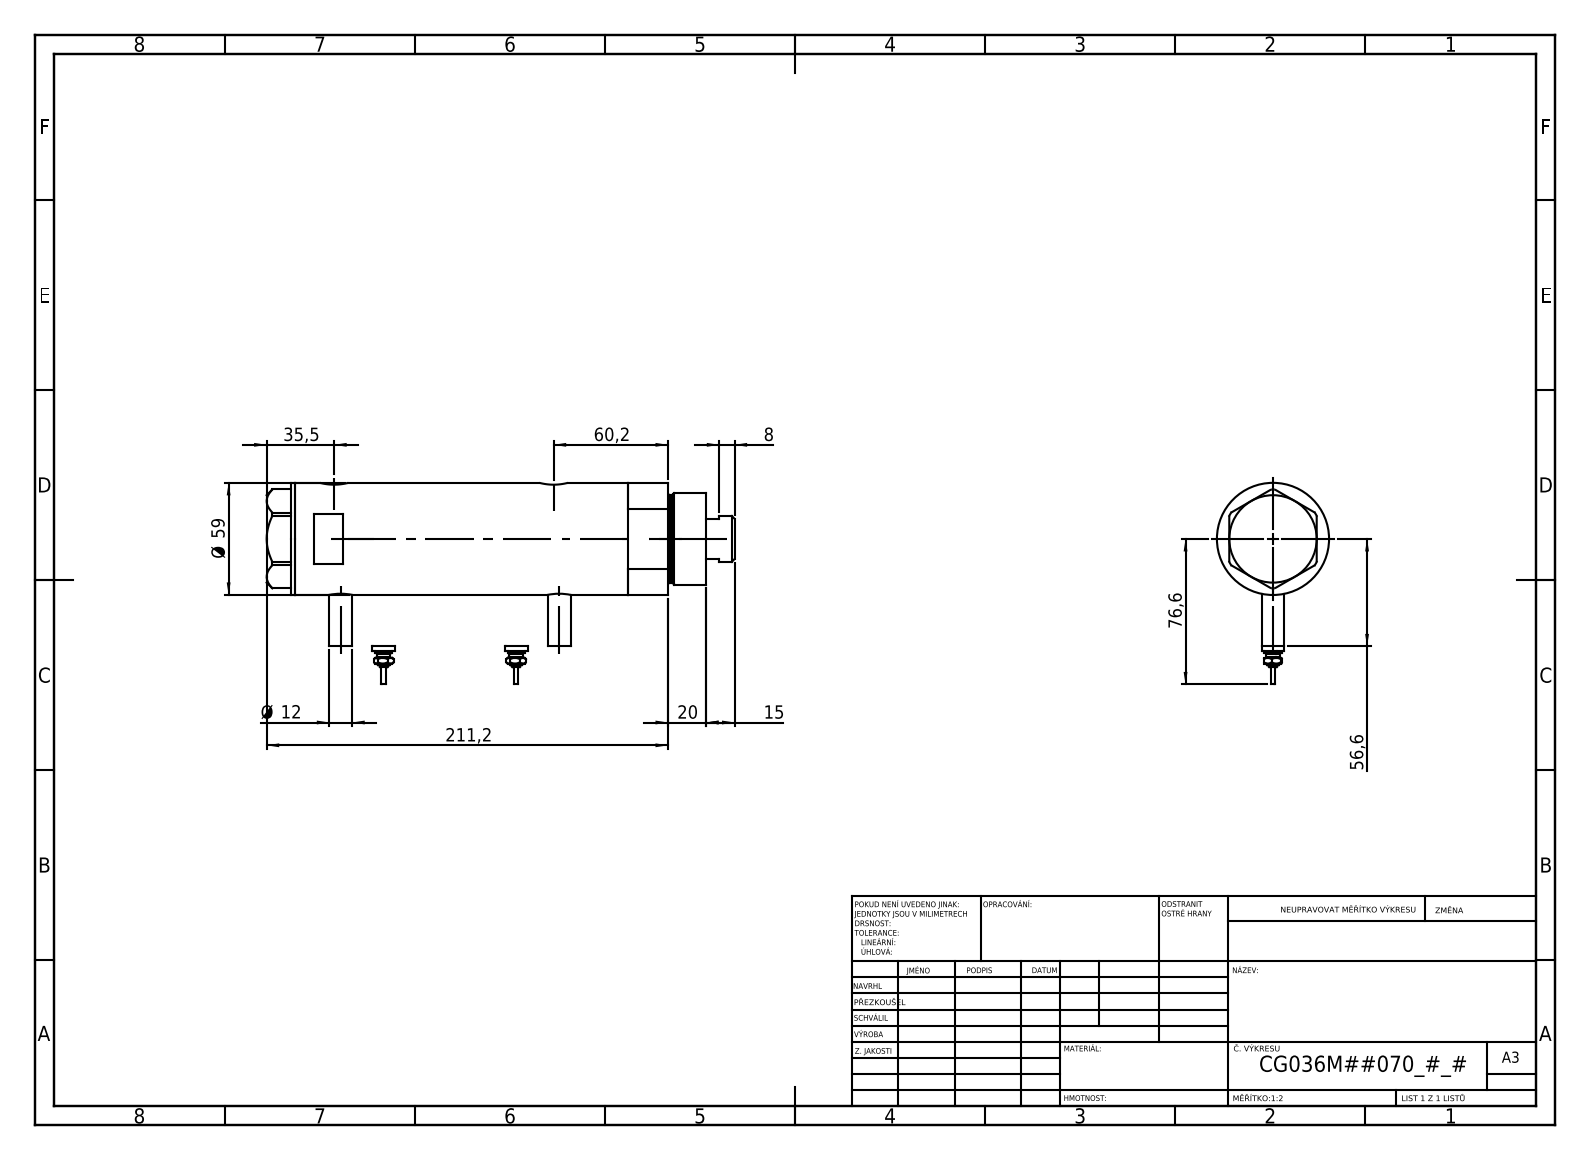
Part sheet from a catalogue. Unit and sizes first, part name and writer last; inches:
Units: inches
Overall size (bounding box): 9.693 × 4.177 × 2.323
Round holes (diameter × count): ⌀0.383 ×2, ⌀0.492 ×2, ⌀0.591 ×2, ⌀0.335 ×1, ⌀0.984 ×1, ⌀1.043 ×1, ⌀1.417 ×1, ⌀1.575 ×1, ⌀2.047 ×1
Round bosses / shafts (diameter × count): ⌀0.472 ×4, ⌀0.354 ×2, ⌀0.276 ×2, ⌀0.177 ×2, ⌀0.098 ×2, ⌀2.323 ×1, ⌀1.89 ×1, ⌀1.811 ×1
Main face-to-face distances: 5.402, 0.925, 4.476, 0.591, 1.516, 5.992, 0.079, 9.102, 8.512, 7.587
Hole centre spacings: 0.114, 0.138, 4.409, 4.524, 4.547, 4.661
Volume: 34.76 in³ · Surface area: 180.5 in²
Bodies: 6 solids, 212 faces (79 planar, 69 cylindrical, 64 other)
Part name (STEP PRODUCT): V270CG_FRONT; V270CG_MIDDLE; V270CG_VC; Switch (+1 more)
STEP written by: SolidWorks 2019 (CONFIG_CONTROL_DESIGN)
